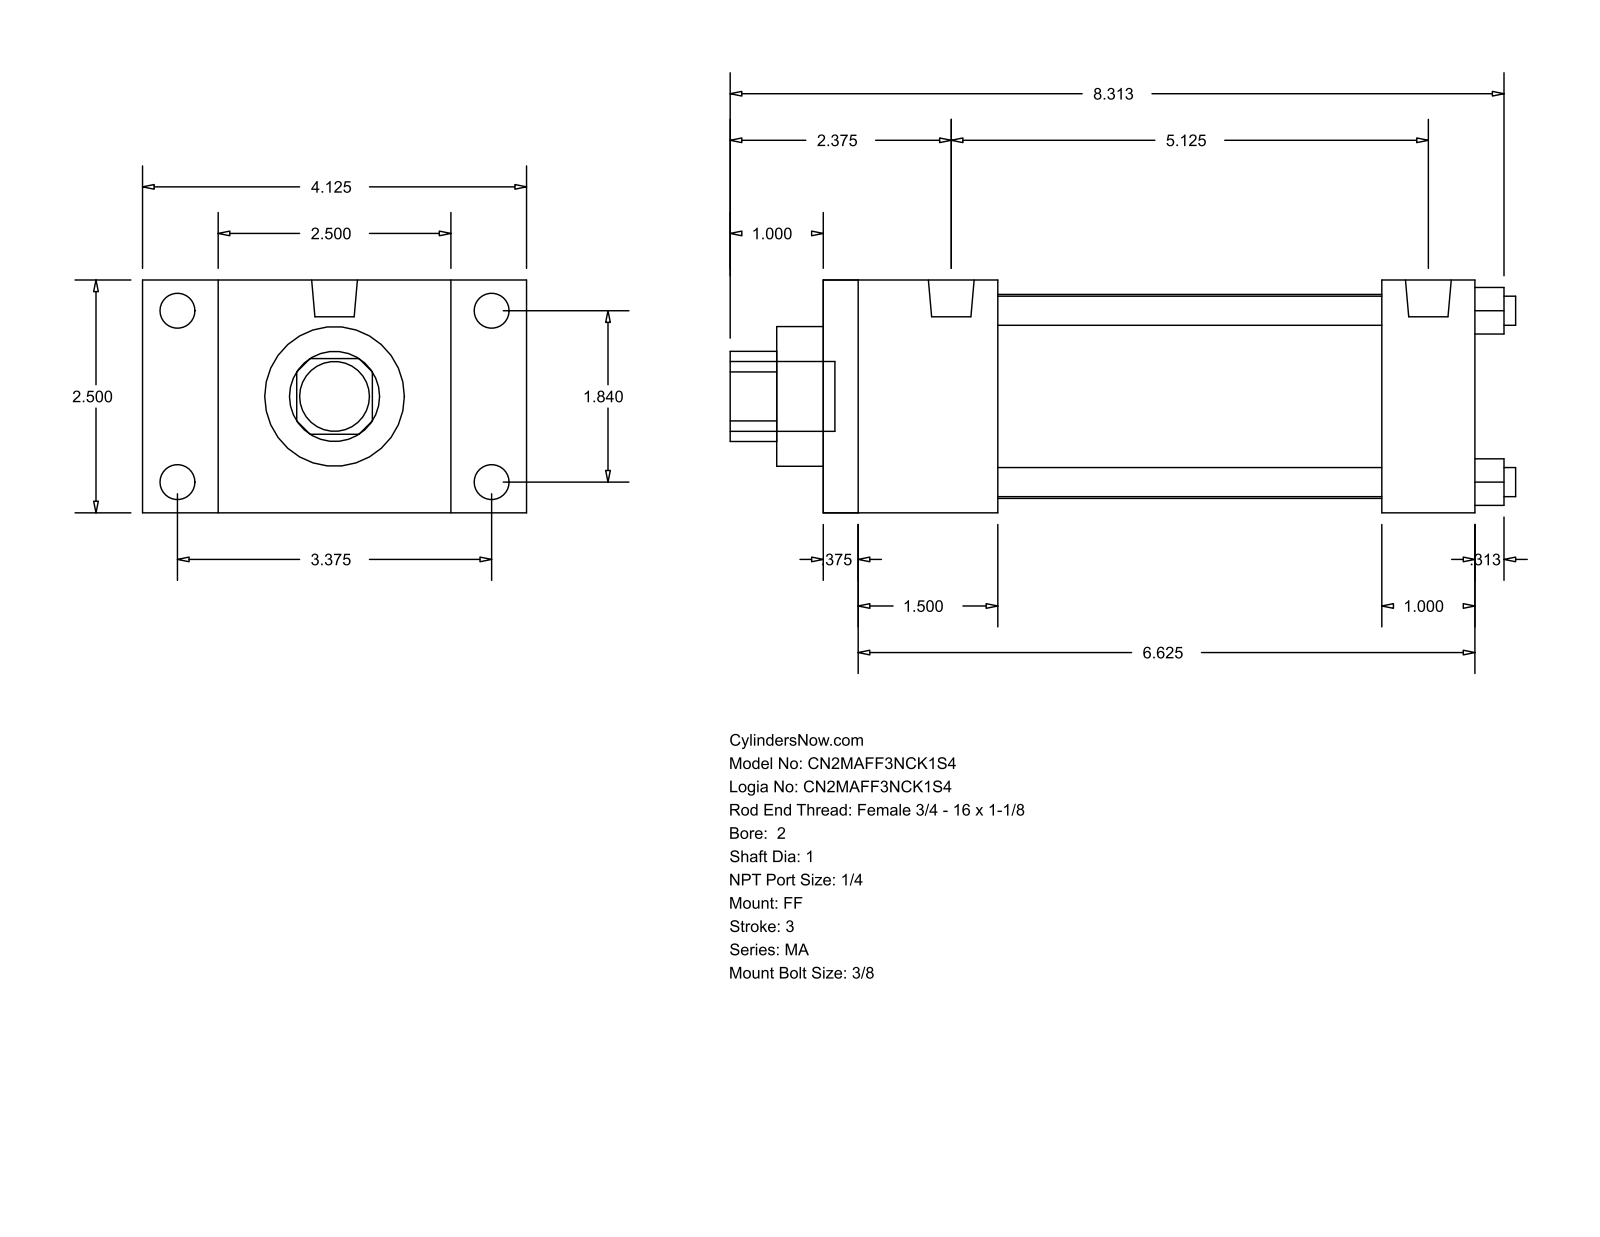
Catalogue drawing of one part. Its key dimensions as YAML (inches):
part_name: "MA_FF__0200_1"
step_written_by: "GSSL Pune (CONFIG_CONTROL_DESIGN)"
units: inches
bodies: {solids: 0, faces: 92, planar: 64, cylindrical: 28, other: 0}
overall_size: [8.437, 4.125, 2.5]
round_holes:
  - {diameter: 0.313, count: 4}
  - {diameter: 1, count: 1}
  - {diameter: 1.5, count: 1}
  - {diameter: 2.19, count: 1}
round_bosses_or_shafts:
  - {diameter: 0.375, count: 4}
  - {diameter: 0.313, count: 4}
  - {diameter: 0.492, count: 2}
  - {diameter: 0.75, count: 1}
partial_cylinders:
  - {radius: 0.484, count: 1}
face_to_face_distances: [2.5, 7, 0.375, 6.625, 1, 0.813, 0.5, 1.875, 6, 1.5]
hole_center_spacings: [1.301, 1.84, 2.602]
